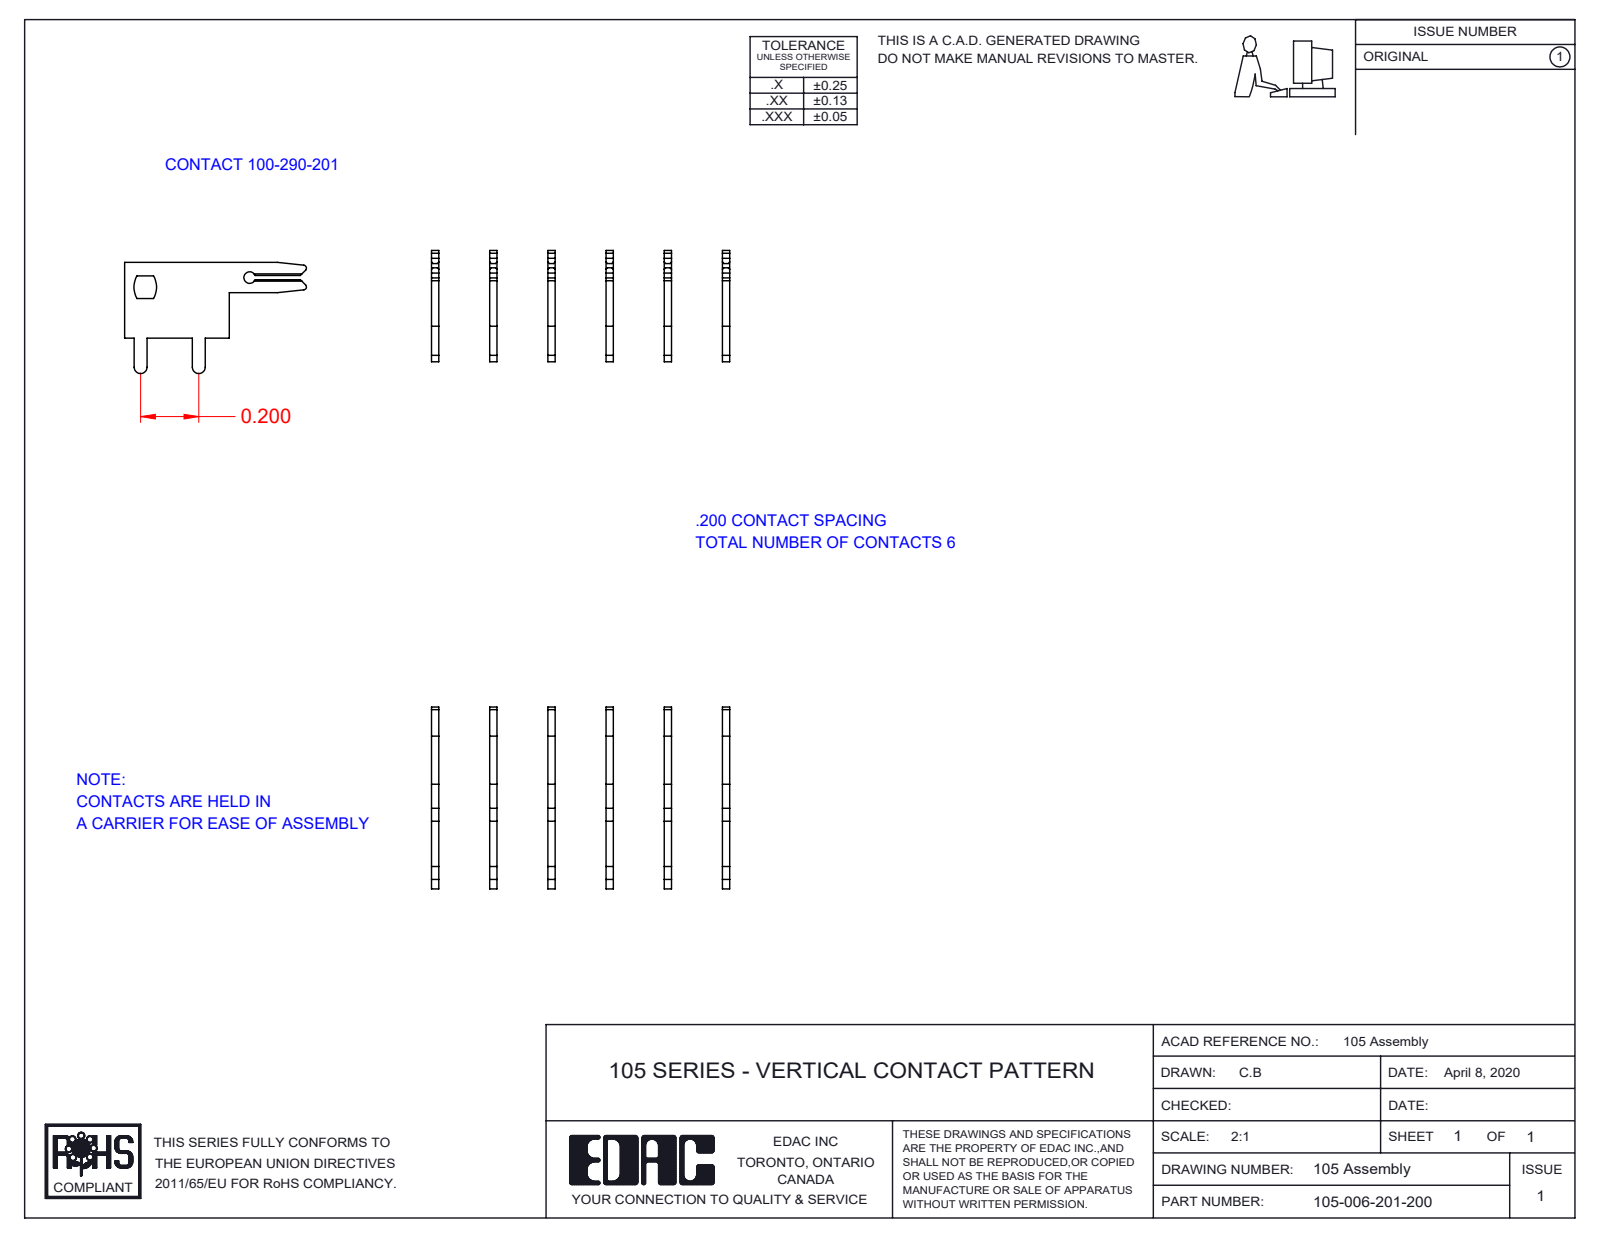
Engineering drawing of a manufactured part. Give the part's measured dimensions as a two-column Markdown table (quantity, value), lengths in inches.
| quantity | value |
| --- | --- |
| part name | 100-290-001_100-290-201; 105-006-201-200 |
| STEP written by | SolidWorks 2016 (CONFIG_CONTROL_DESIGN) |
| units | inches |
| bodies | 6 solids, 210 faces (150 planar, 60 cylindrical, 0 other) |
| overall size | 1.025 × 0.625 × 0.382 |
| volume | 0.018 in³ |
| surface area | 1.869 in² |
| round holes (diameter × count) | 0.04 × 1 |
| partial cylindrical surfaces (radius × count) | 0.01 × 2, 0.022 × 2, 0.078 × 2 |
| main face-to-face distances | 0.2, 0.4, 0.025, 0.6, 0.225, 0.175, 0.425, 0.8, 0.375, 0.625 |
